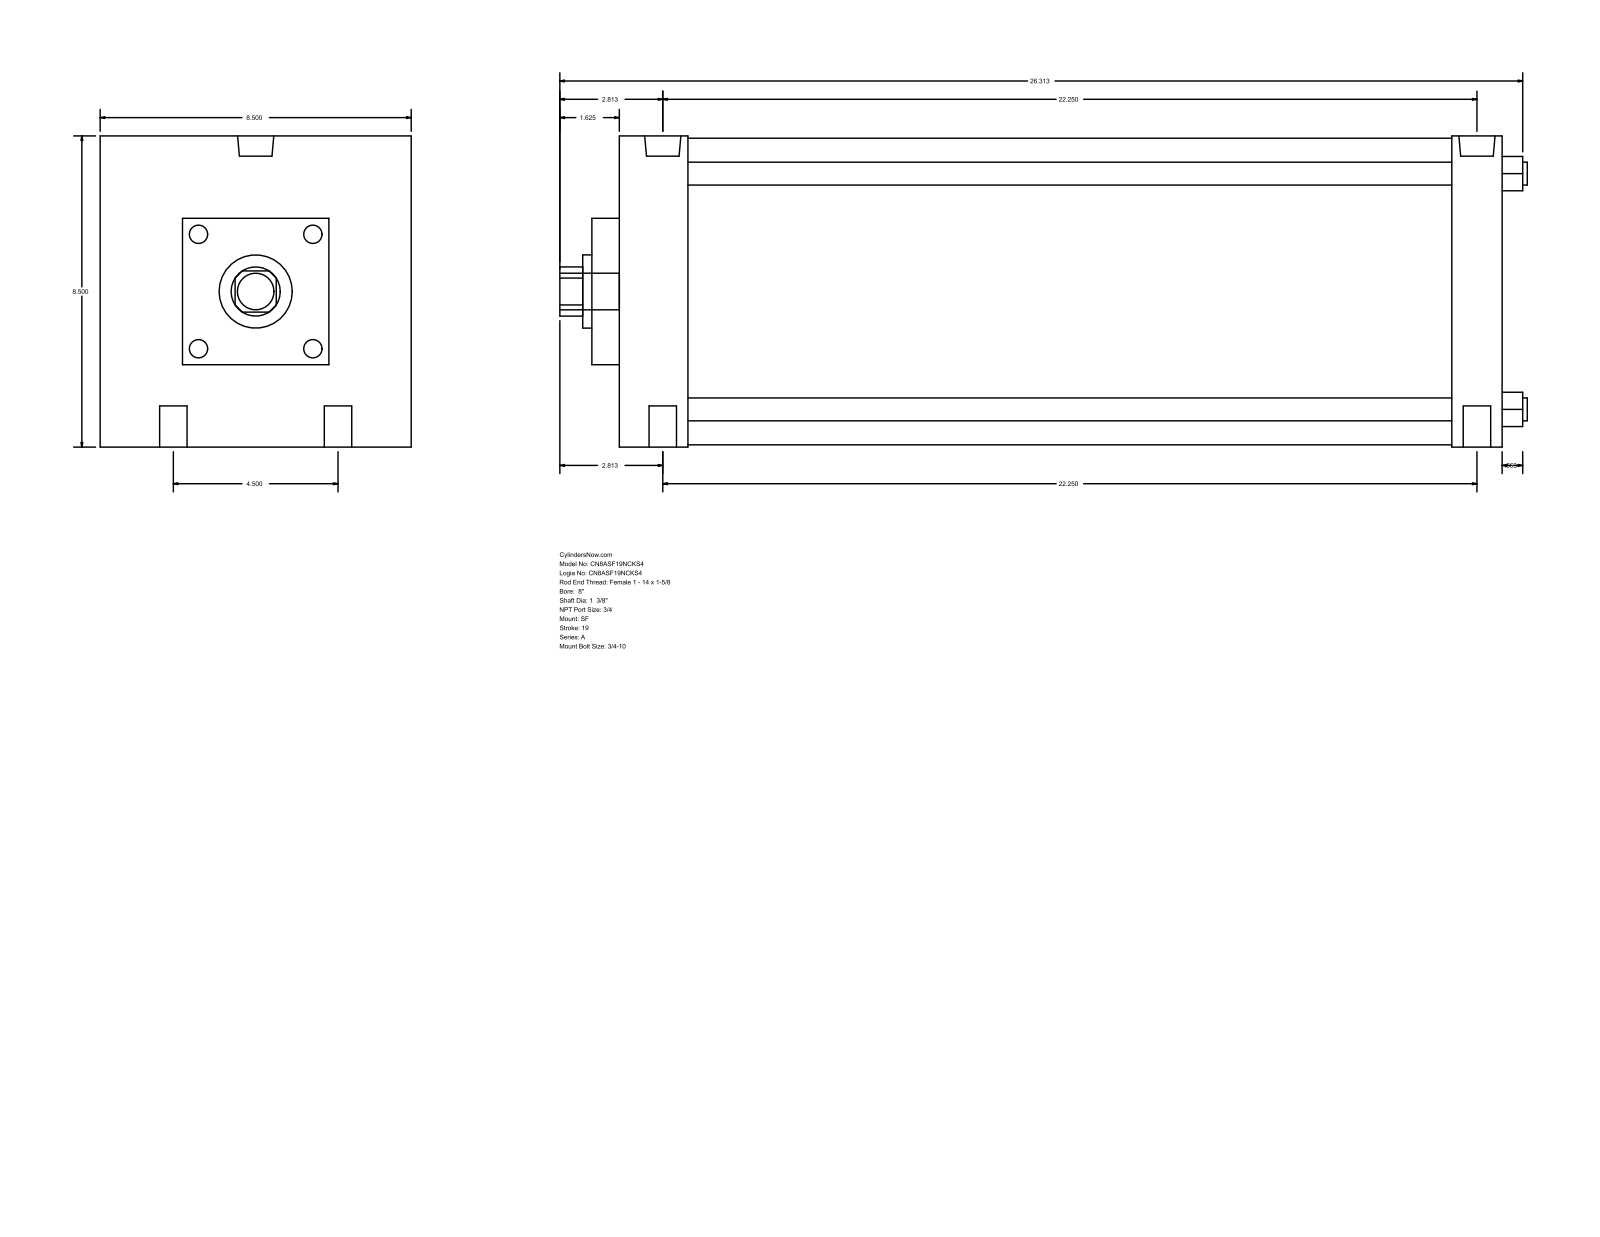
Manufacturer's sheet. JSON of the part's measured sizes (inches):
{"part_name": "A_SF__0800_1.375", "step_written_by": "GSSL Pune (CONFIG_CONTROL_DESIGN)", "units": "inches", "bodies": {"solids": 0, "faces": 93, "planar": 67, "cylindrical": 26, "other": 0}, "overall_size": [26.437, 8.5, 8.5], "round_holes": [[0.75, 4], [0.594, 2], [0.989, 2], [1.375, 1], [2, 1]], "round_bosses_or_shafts": [[0.625, 4], [8.375, 1], [1, 1]], "partial_cylinders_radius": [[0.672, 1]], "face_to_face_distances": [24.125, 8.5, 1.875, 22.75, 20.875, 22.25, 1.375, 0.75, 2.625, 23.5], "hole_center_spacings": [2.25, 22.363, 22.25, 4.5, 22.7, 21.75]}
